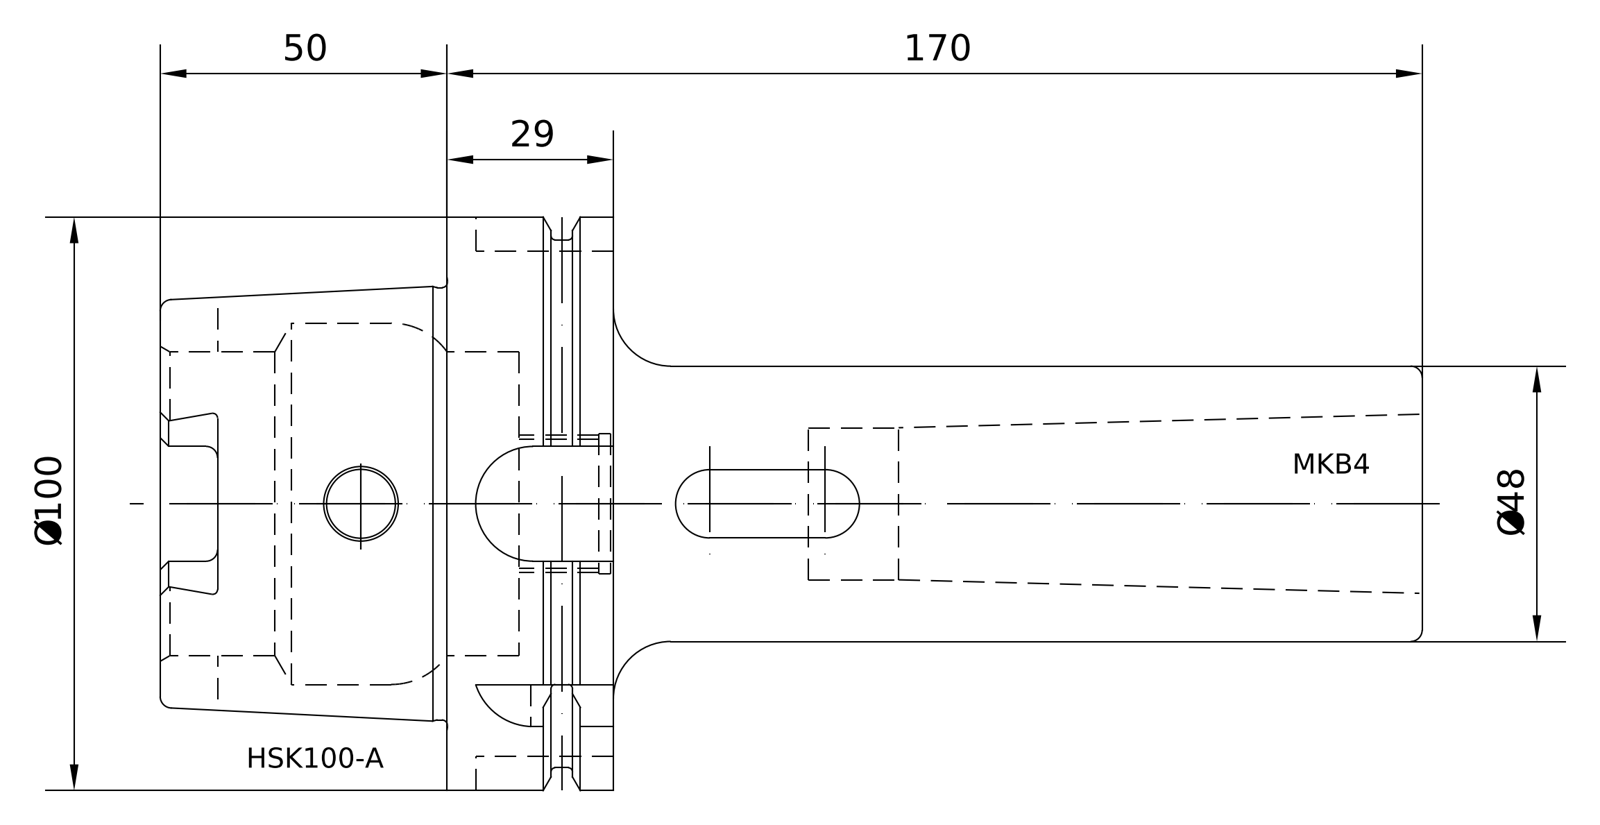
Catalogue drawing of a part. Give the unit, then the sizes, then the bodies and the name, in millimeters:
Units: millimetres
Overall size (bounding box): 220 × 100 × 100
Round holes (diameter × count): ⌀10 ×1, ⌀12 ×1, ⌀22.5 ×1, ⌀24 ×1, ⌀24.32 ×1, ⌀24.5 ×1, ⌀26.5 ×1, ⌀53 ×1, ⌀63 ×1
Round bosses / shafts (diameter × count): ⌀100 ×1, ⌀92 ×1, ⌀75.36 ×1, ⌀48 ×1
Partial cylindrical surfaces — rounded edges, fillets, slot ends (radius × count): R2 ×6, R5 ×4, R8 ×1, R10 ×1, R11 ×1
Main face-to-face distances: 29, 12.5, 16.5, 50, 62.5, 79, 220, 170, 157.5, 141
Volume: 444 100 mm³ · Surface area: 80 147 mm²
Bodies: 1 solid, 174 faces (50 planar, 51 cylindrical, 73 other)
Part name (STEP PRODUCT): A100-080-04
STEP written by: PRO/ENGINEER BY PARAMETRIC TECHNOLOGY CORPORATION, 2010430 (CONFIG_CONTROL_DESIGN)
